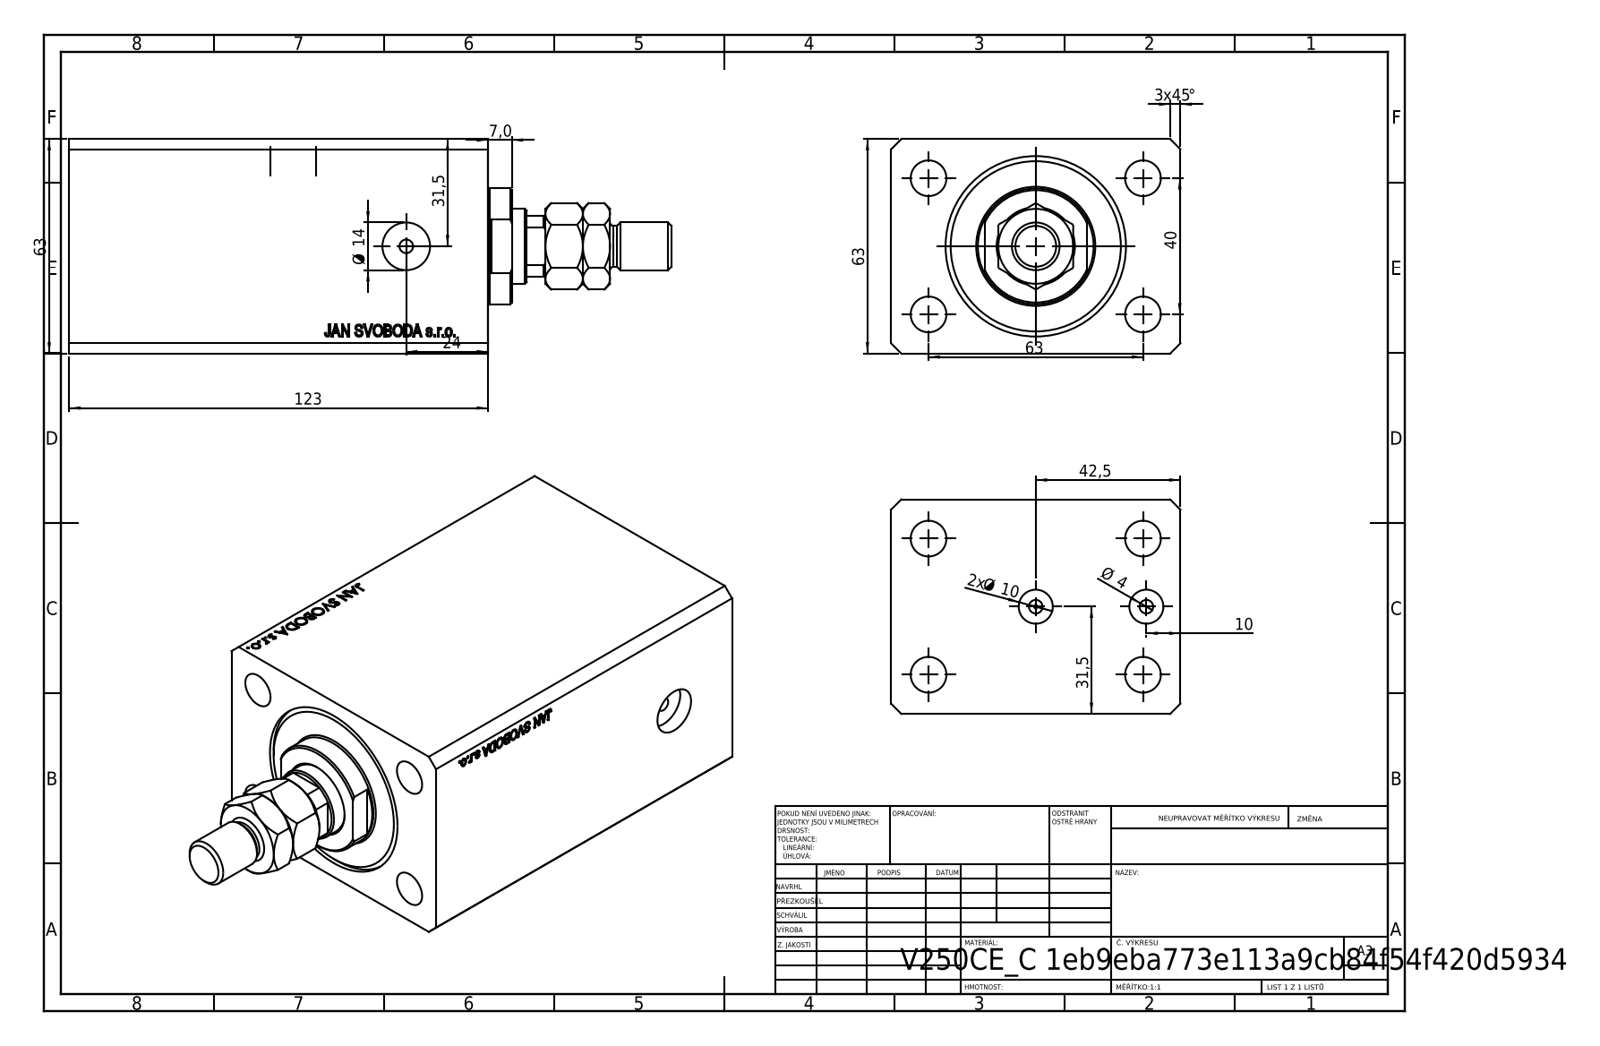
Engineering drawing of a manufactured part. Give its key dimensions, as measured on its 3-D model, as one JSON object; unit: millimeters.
{"part_name": "V250CE_VC_C; MTA; V250CE_C_Body; V250CE_C_VCP", "step_written_by": "SolidWorks 2019 (CONFIG_CONTROL_DESIGN)", "units": "millimeters", "bodies": {"solids": 4, "faces": 917, "planar": 443, "cylindrical": 50, "other": 424}, "overall_size": [176.9, 85, 63], "volume_mm3": 583575, "surface_area_mm2": 107795, "round_holes": [[4, 4], [10.5, 4], [10, 2], [14, 2], [1.25, 1], [12.5, 1], [22, 1], [40, 1], [53, 1]], "round_bosses_or_shafts": [[34, 1], [14, 1], [12, 1]], "partial_cylinders_radius": [[10.5, 1]], "face_to_face_distances": [63, 85, 123, 95.9, 27.1, 11.4, 84.5, 111.6, 100.4, 50], "hole_center_spacings": [37.31, 20.02, 40, 63, 67.05, 74.63, 32.5, 75]}
